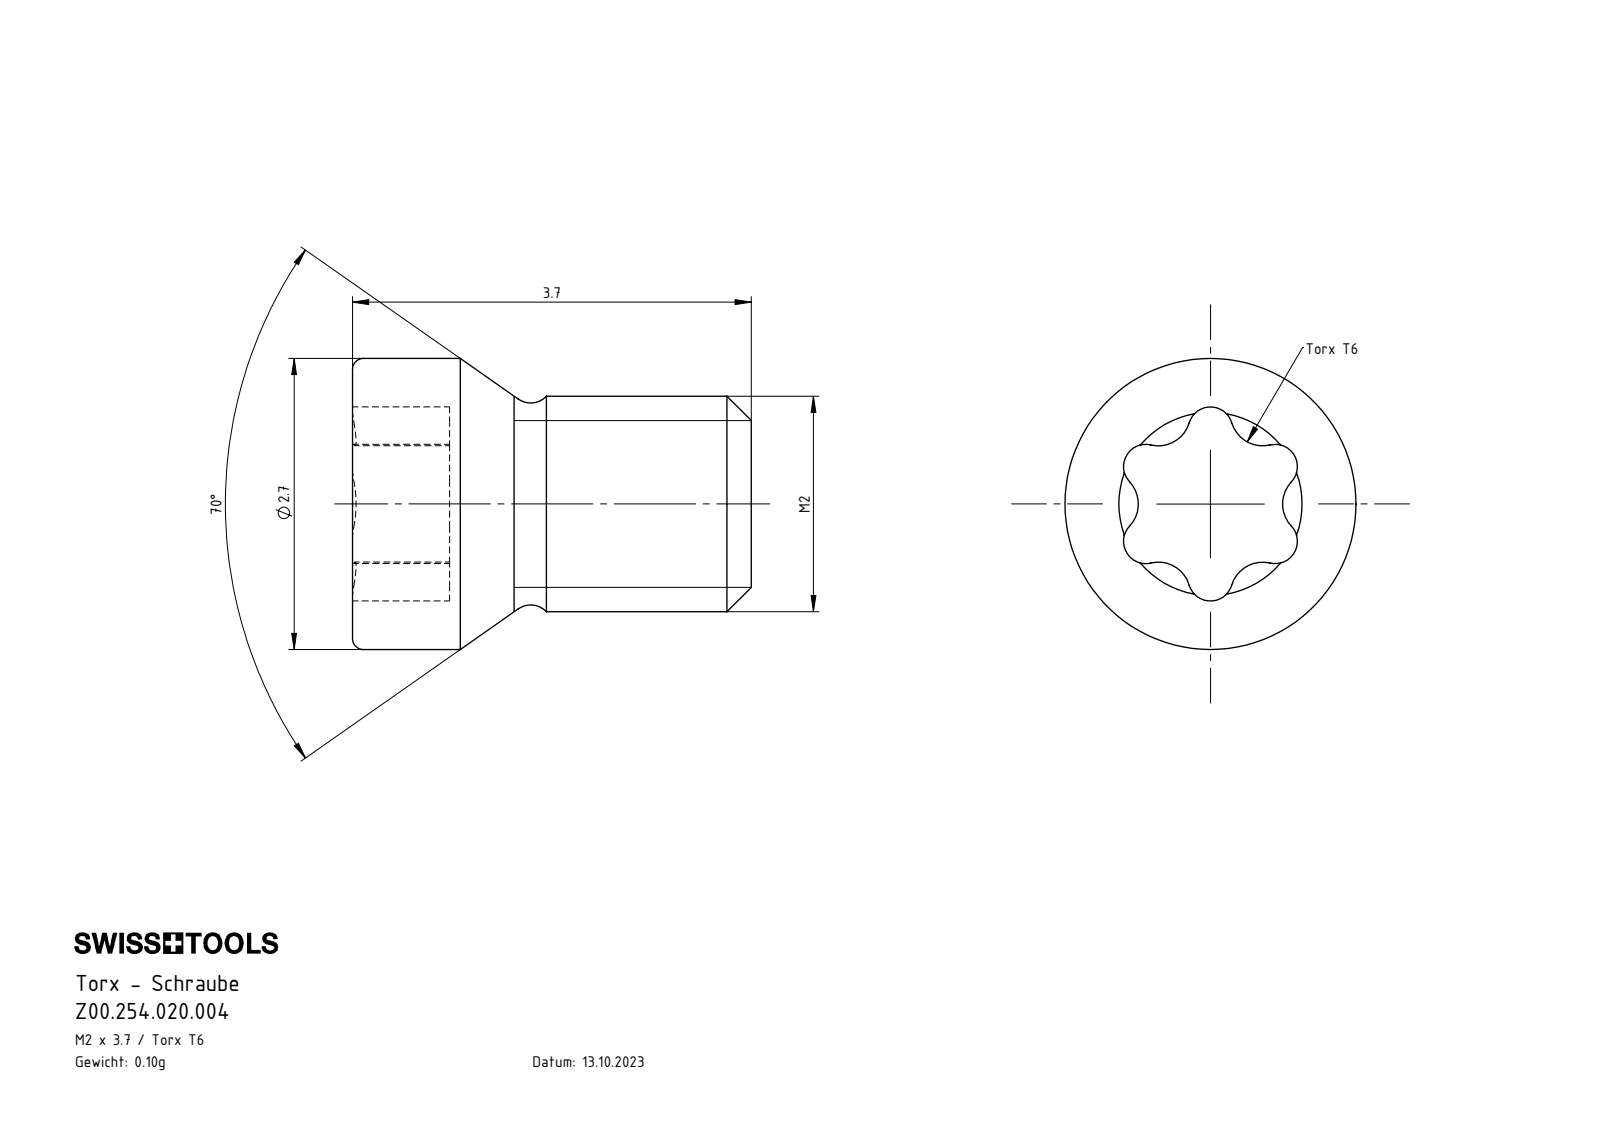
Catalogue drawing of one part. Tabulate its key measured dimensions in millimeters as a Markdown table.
| quantity | value |
| --- | --- |
| part name | Z00.254.020.004 |
| STEP written by | SolidWorks 2022 (AUTOMOTIVE_DESIGN) |
| units | millimeters |
| bodies | 1 solid, 41 faces (3 planar, 19 cylindrical, 19 other) |
| overall size | 3.7 × 2.7 × 2.7 |
| volume | 13 mm³ |
| surface area | 40 mm² |
| round bosses / shafts (diameter × count) | 2.7 × 1, 2 × 1 |
| partial cylindrical surfaces (radius × count) | 0.21 × 6, 0.3 × 6 |
| main face-to-face distances | 0.9, 3.7, 2.8 |
